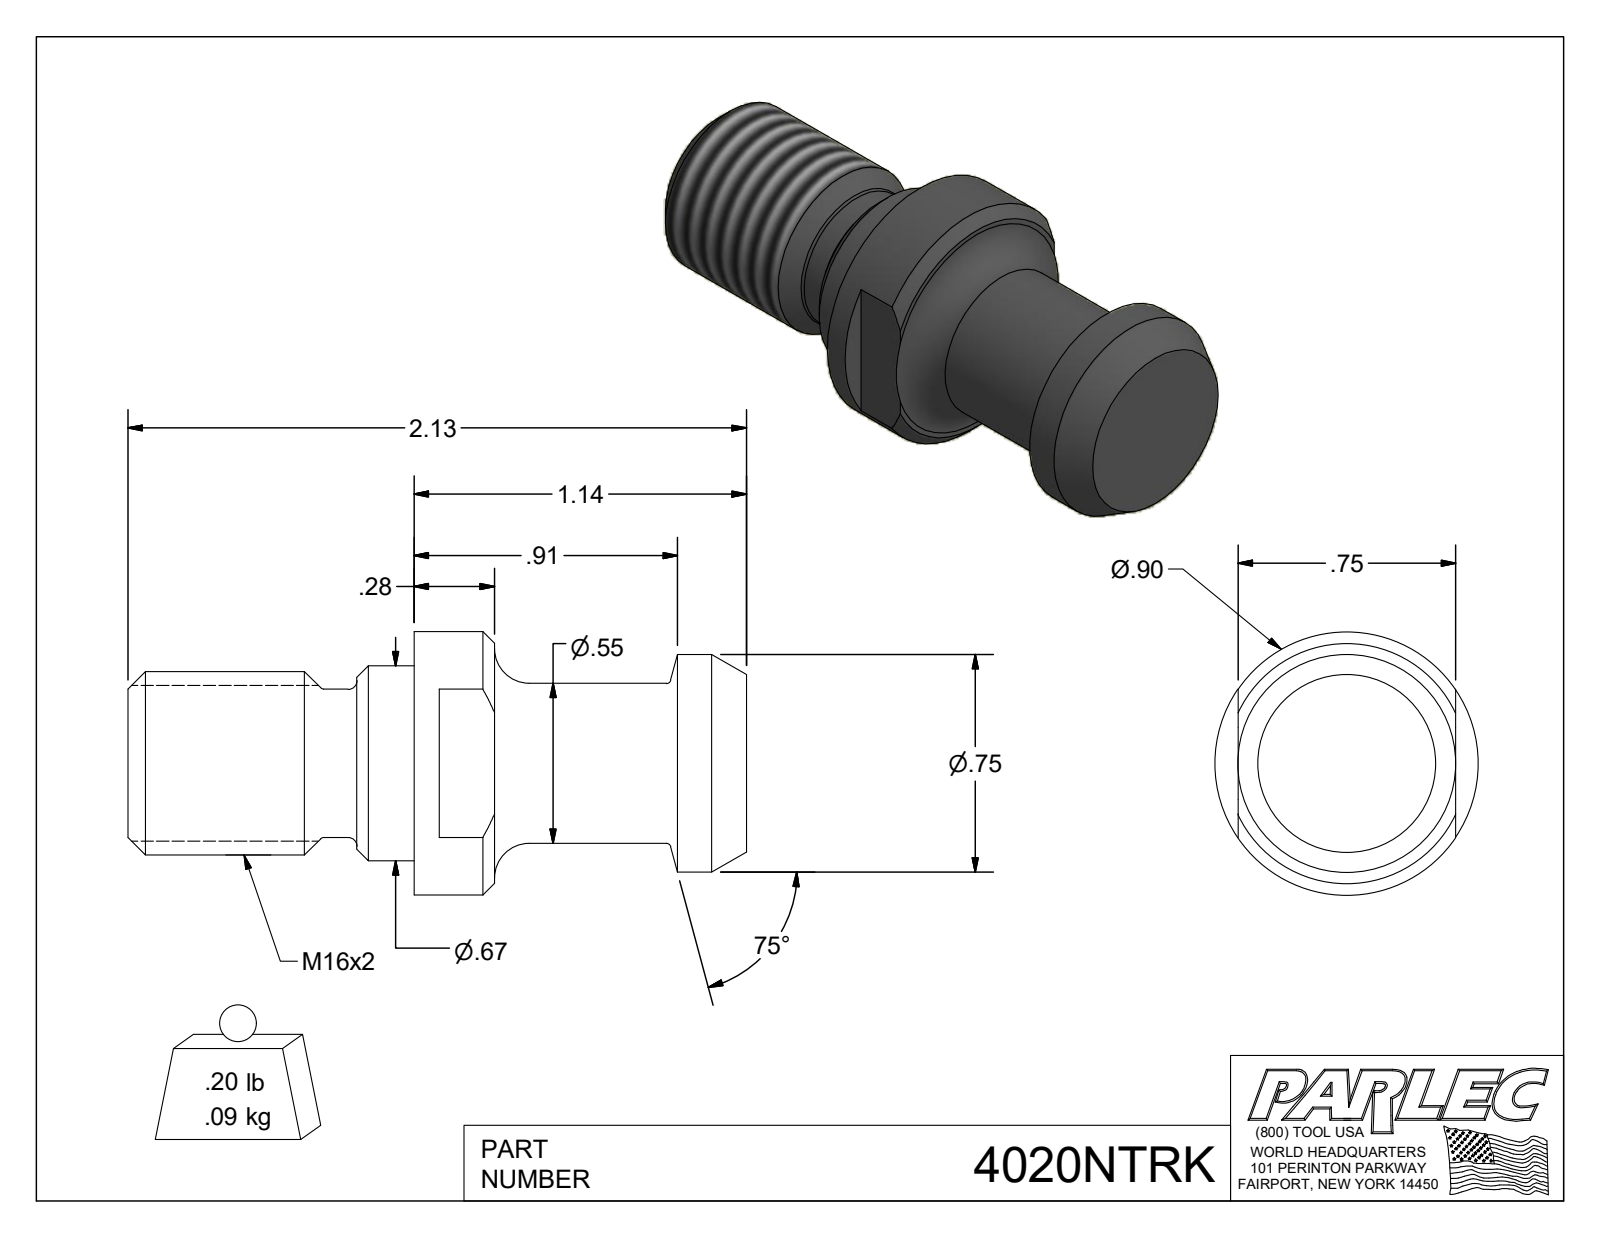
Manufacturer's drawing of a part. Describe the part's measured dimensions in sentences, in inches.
The part is named "4020NTRK". Its 3-D file was written by "Autodesk Inventor 2018 (AUTOMOTIVE_DESIGN)". It is 1 solid with 29 faces: 12 planar, 6 cylindrical and 11 other. Overall it measures 2.126 by 0.905 by 0.905 inches. Its volume is 0.712 cubic inches and its surface area 5.734 square inches. Round bosses or shafts: 1 of diameter 0.905, 1 of diameter 0.748, 1 of diameter 0.669, 1 of diameter 0.63, 1 of diameter 0.55, 1 of diameter 0.51. The main face-to-face distances are 1.142, 0.984, 2.126, 0.748, 1.07, 0.086, 1.056, 1.26, 0.276, 0.19.
